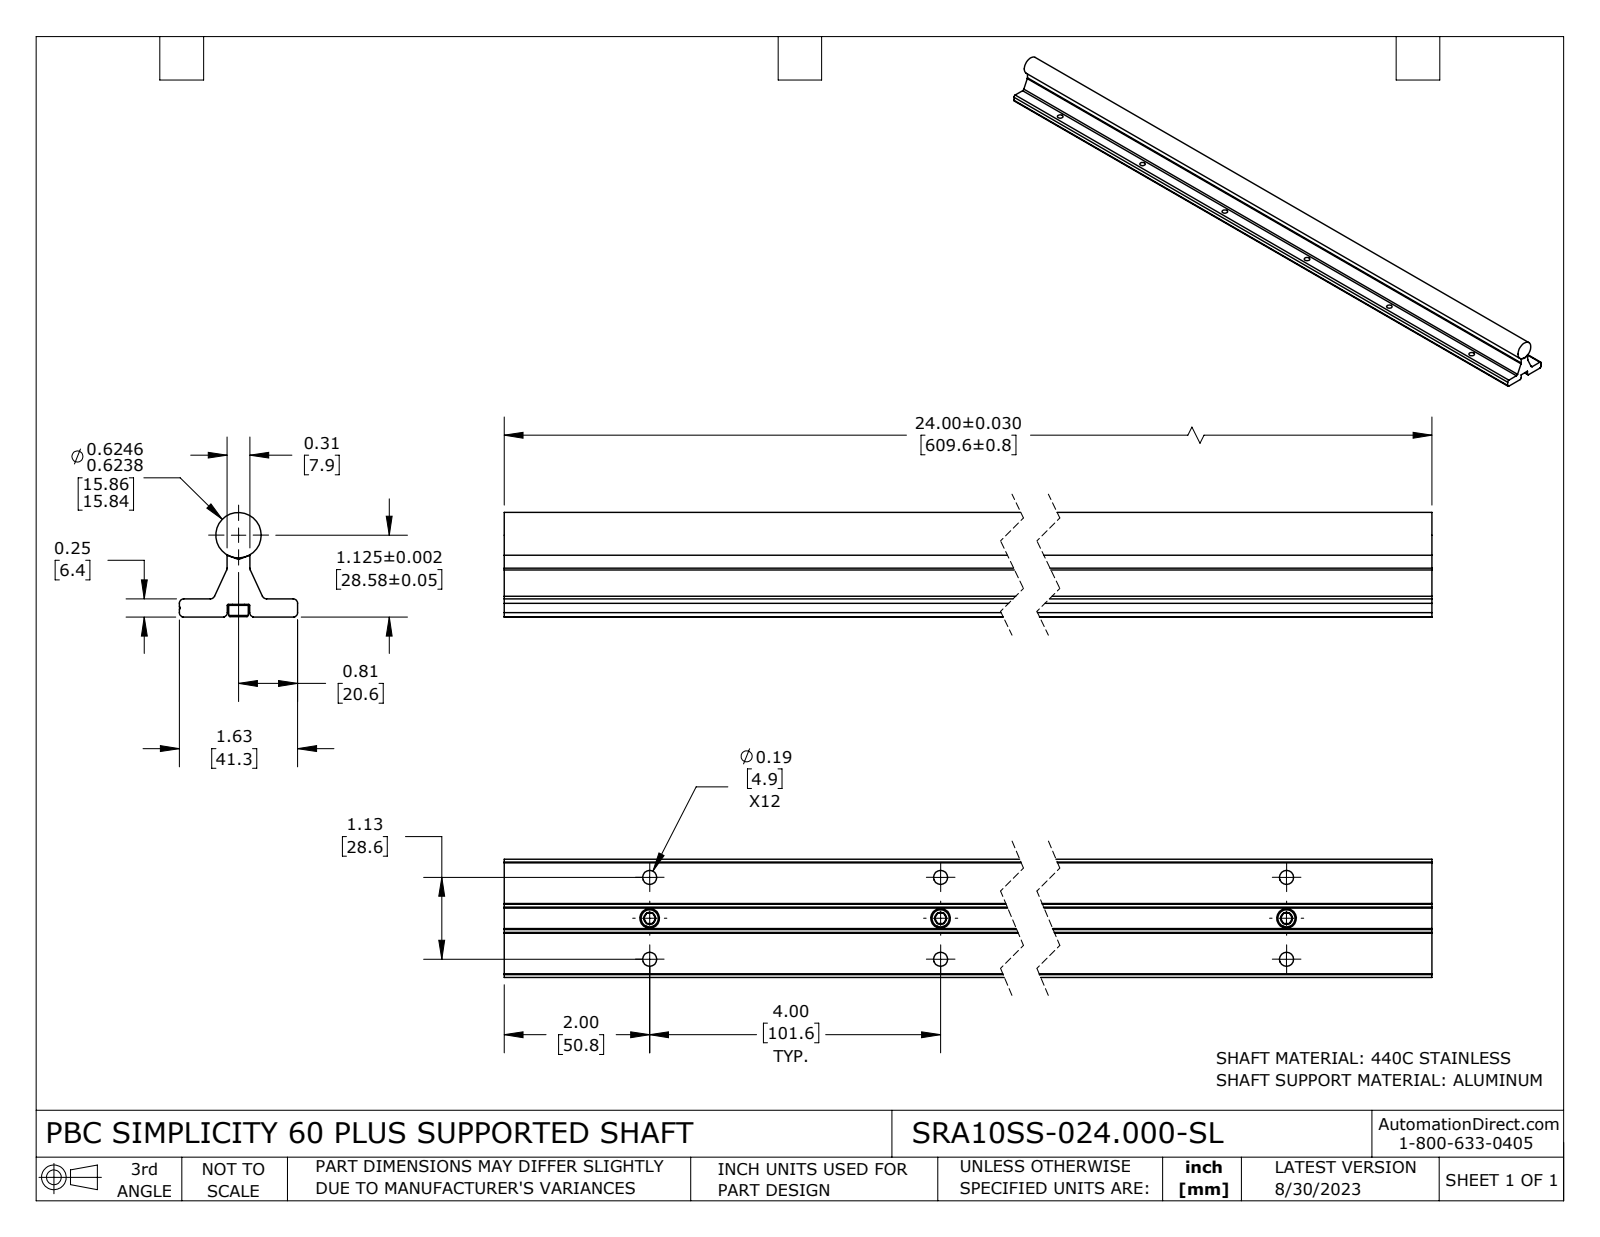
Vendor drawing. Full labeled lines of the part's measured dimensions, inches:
Part name (STEP PRODUCT): SRA10SS-024.000-SL
STEP written by: SolidWorks 2021 (CONFIG_CONTROL_DESIGN)
Units: inches
Bodies: 8 solids, 281 faces (93 planar, 98 cylindrical, 90 other)
Overall size (bounding box): 24 × 1.625 × 1.438
Volume: 21.78 in³ · Surface area: 174.1 in²
Round holes (diameter × count): ⌀0.194 ×18, ⌀0.141 ×6, ⌀0.188 ×6
Round bosses / shafts (diameter × count): ⌀0.27 ×6, ⌀0.165 ×6, ⌀0.625 ×1
Partial cylindrical surfaces — rounded edges, fillets, slot ends (radius × count): R0.06 ×6, R0.015 ×2, R0.062 ×2, R0.063 ×2
Main face-to-face distances: 0.25, 0.174, 0.076, 0.656, 0.969, 0.657, 0.968, 0.311, 0.313, 1.625
Hole centre spacings: 4.039, 8.02, 4, 0.563, 8, 12.013, 4.155, 12
